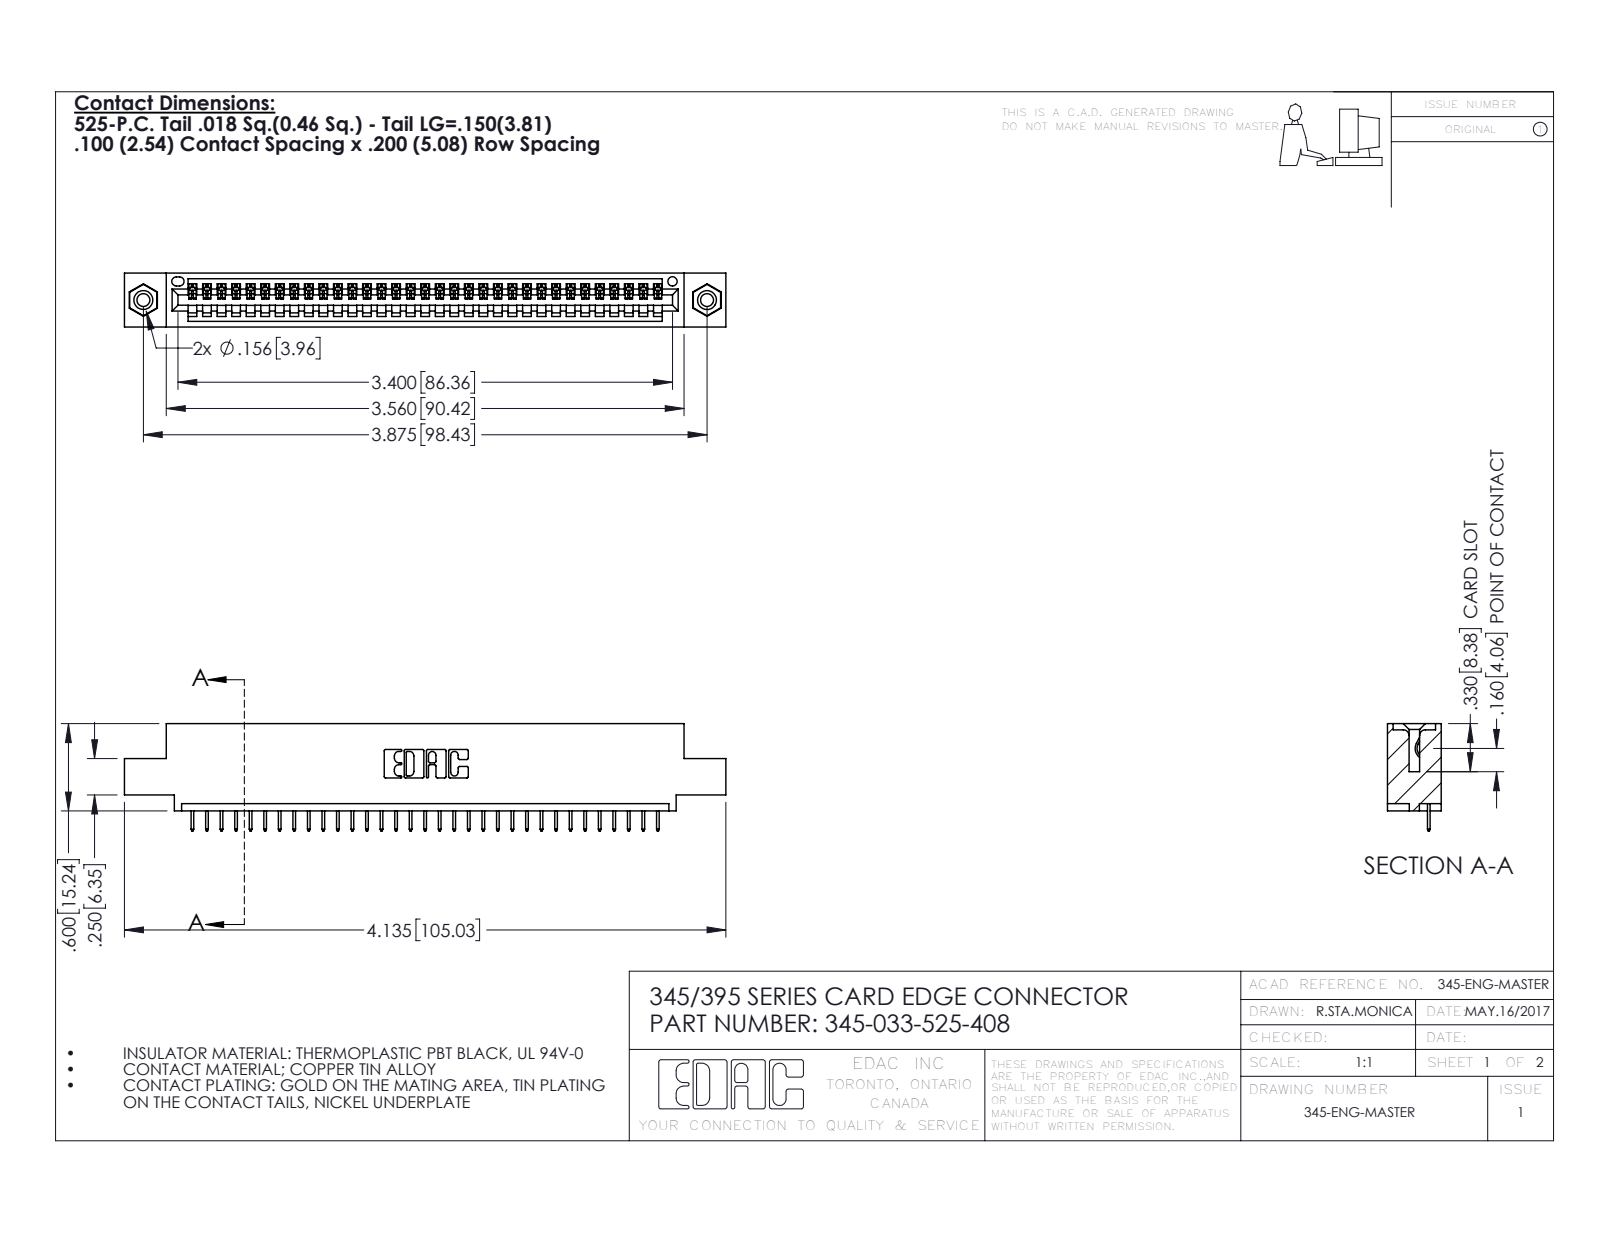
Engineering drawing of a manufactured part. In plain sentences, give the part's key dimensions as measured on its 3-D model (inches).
The part is named "345-250-001_345-250-003-102; 345-292-001_345-293-125; 345 Part_0.110 Offset - 0.156 Dia-TI; 345-033-525-408". Its 3-D file was written by "SolidWorks 2020 (CONFIG_CONTROL_DESIGN)". It is 36 solids with 2236 faces: 1634 planar, 586 cylindrical and 16 other. Overall it measures 4.135 by 0.737 by 0.37 inches. Its volume is 0.591 cubic inches and its surface area 19.22 square inches. Round holes: 2 of diameter 0.089, 2 of diameter 0.125, 2 of diameter 0.156, 1 of diameter 0.064. Round bosses or shafts: 2 of diameter 0.155. Partial cylindrical surfaces (rounded edges, fillets, slot ends): 66 of radius 0.006, 22 of radius 0.01, 6 of radius 0.007, 6 of radius 0.031, 3 of radius 0.026, 2 of radius 0.031, 2 of radius 0.04, 1 of radius 0.014. The main face-to-face distances are 0.072, 0.298, 0.37, 0.2, 0.098, 0.272, 0.025, 0.225, 0.072, 0.149. The hole center spacings are 0.27, 3.64, 3.875.
